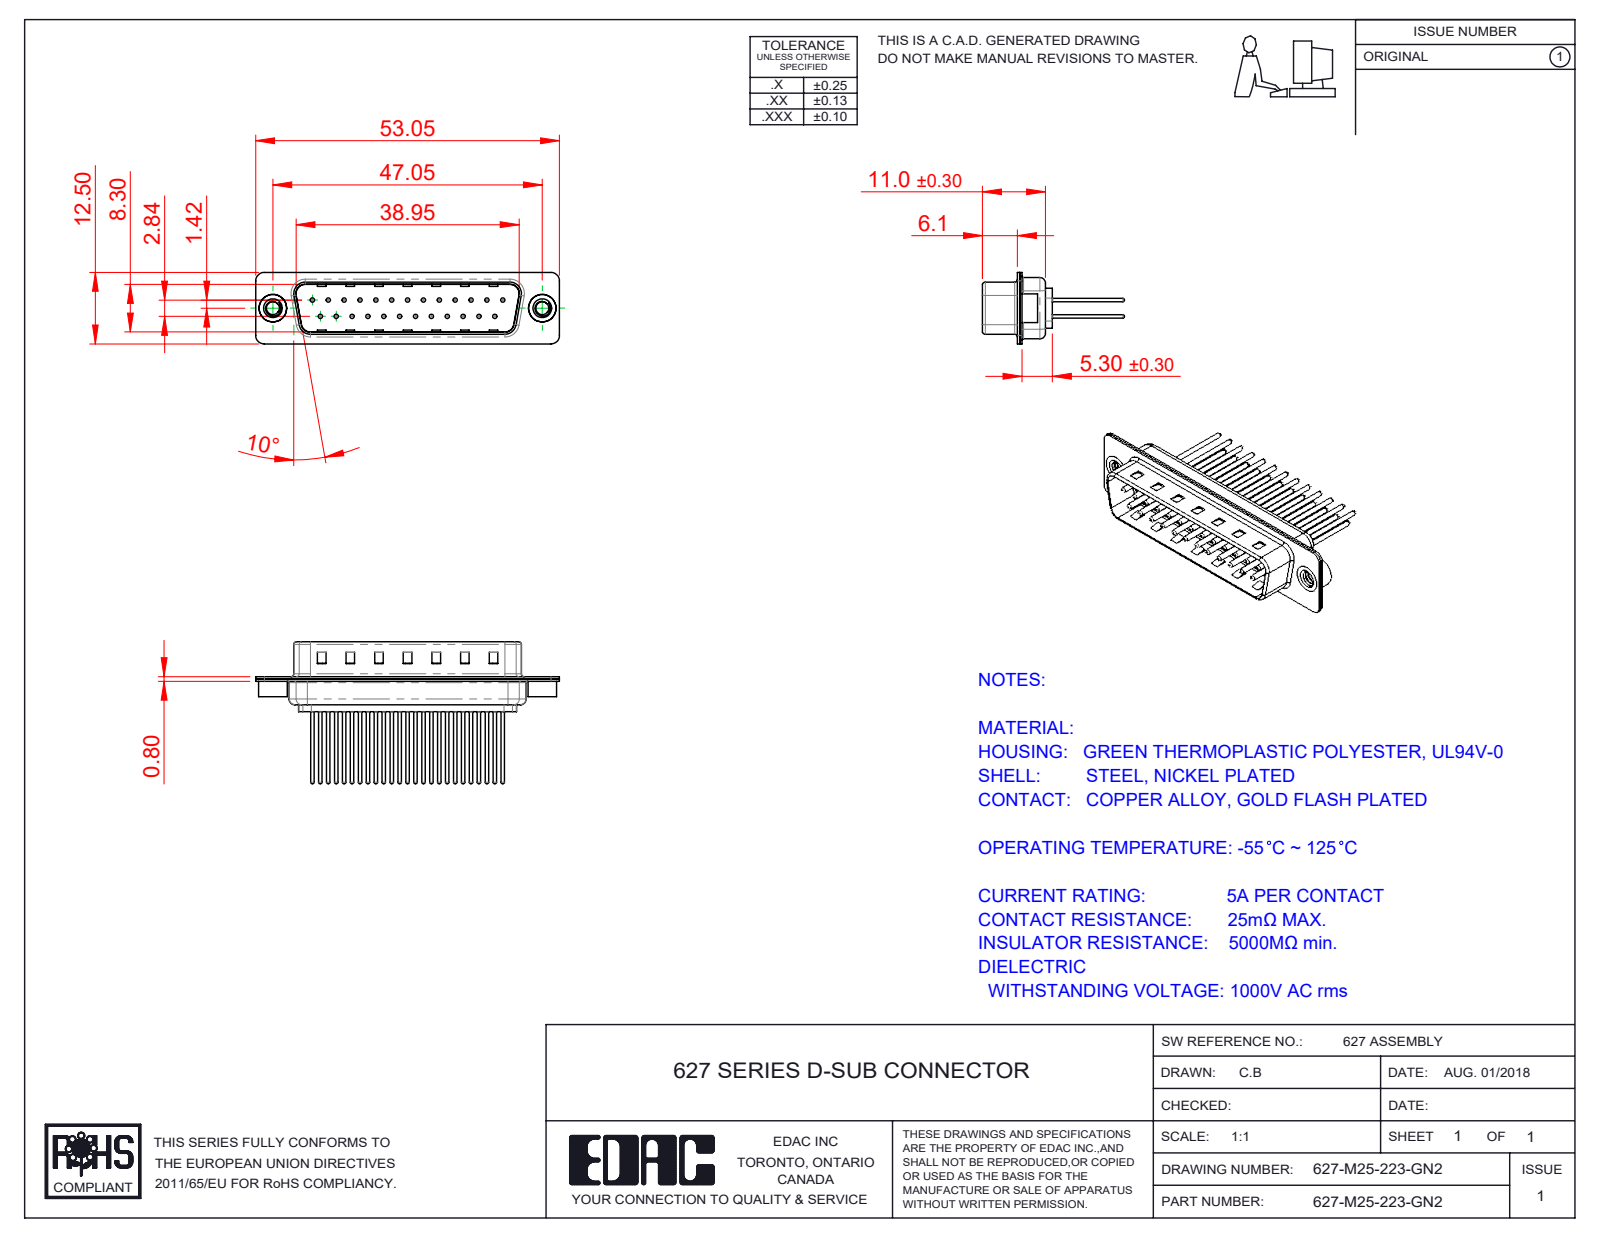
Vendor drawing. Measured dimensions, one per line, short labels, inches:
name: 627M Shell Front_25 Contacts; 627M Contact Row 2_23; 627M Shell Rear_25 Contacts; 627M 4-40 Threaded Rivet (+3 more)
written by: SolidWorks 2020 (CONFIG_CONTROL_DESIGN)
unit: in
bodies: 30 solids, 1301 faces (346 planar, 487 cylindrical, 468 other)
size: 2.089 × 0.975 × 0.492
volume: 0.169 in³; area: 11.11 in²
holes: 25× ⌀0.03, 25× ⌀0.063, 25× ⌀0.079, 2× ⌀0.089, 2× ⌀0.157, 2× ⌀0.189
bosses: 25× ⌀0.059, 25× ⌀0.024, 2× ⌀0.197, 2× ⌀0.193
rounds: 16× R0.059, 12× R0.079, 8× R0.02, 8× R0.063, 4× R0.01, 4× R0.024, 4× R0.026, 4× R0.035
face distances: 0.016, 0.031, 0.374, 0.358, 0.343, 0.39, 0.047, 0.24, 0.224, 0.03
hole spacings: 0.124, 0.109, 0.218, 0.327, 0.436, 0.545, 0.654, 0.198
